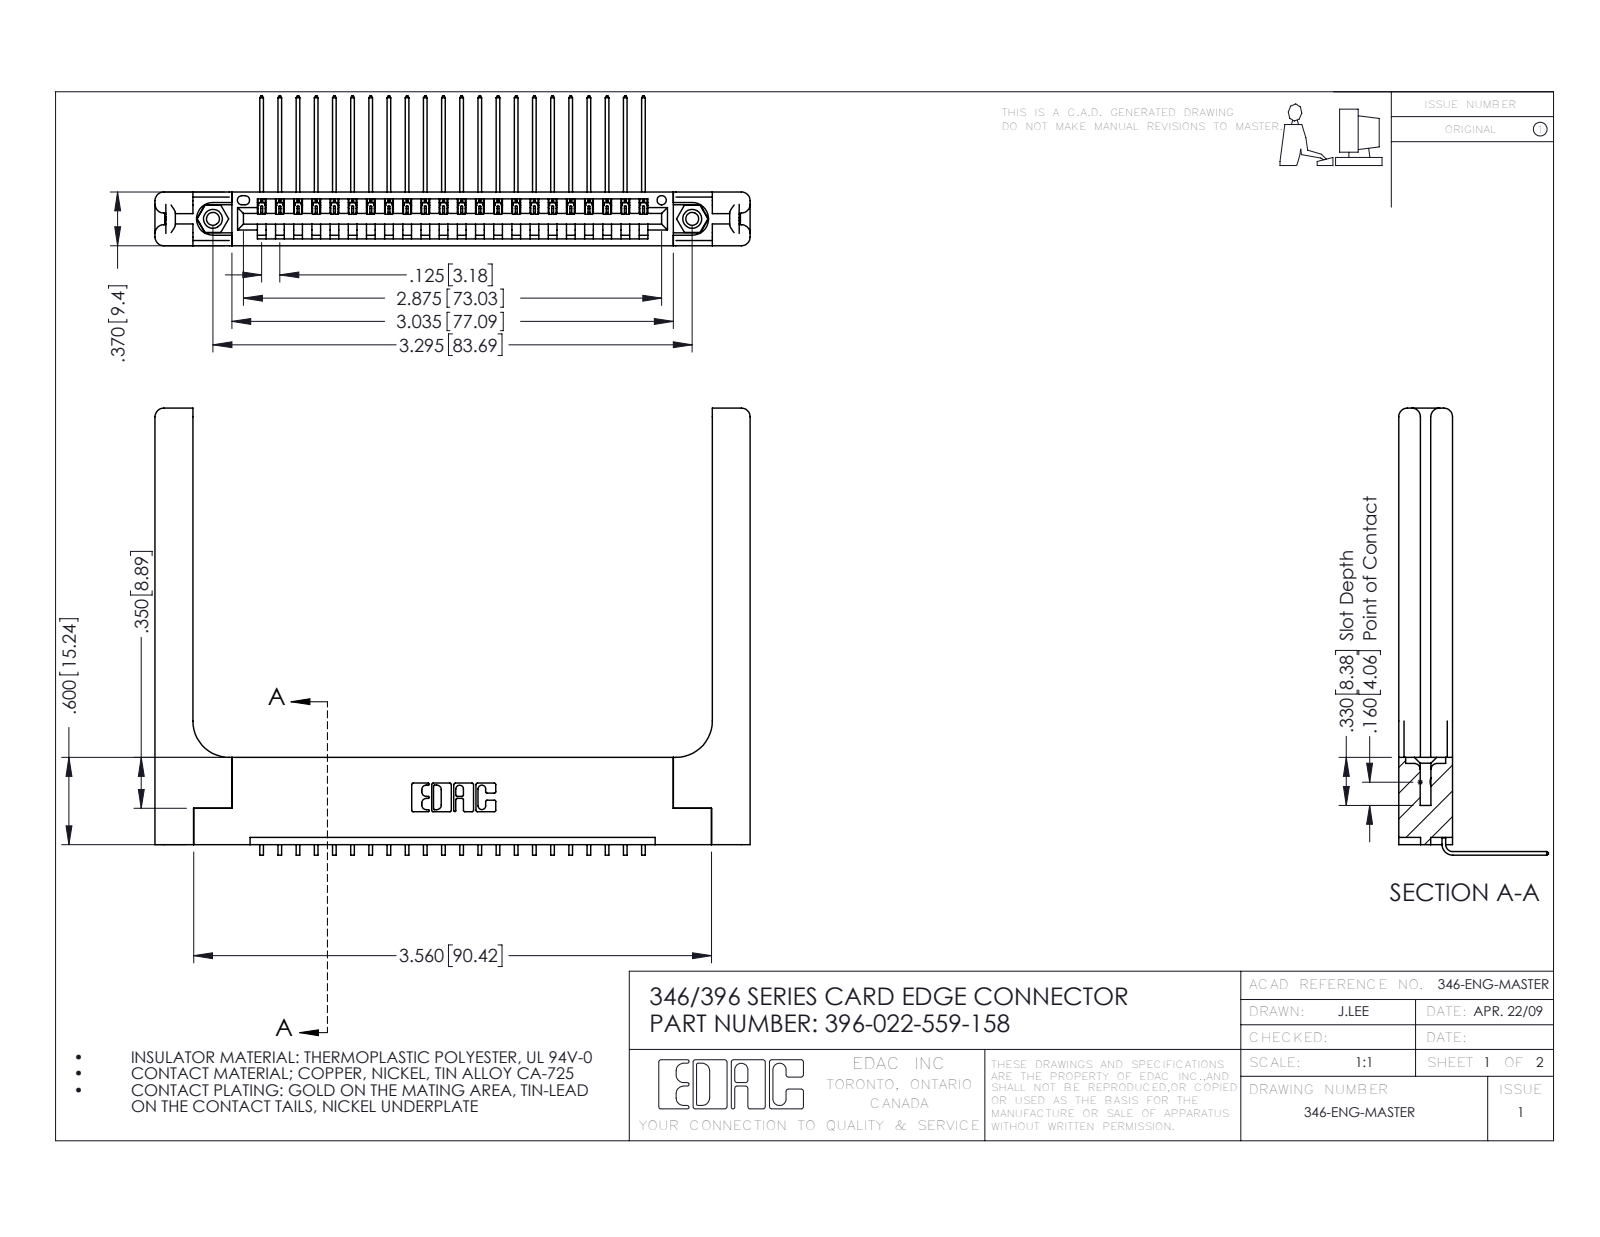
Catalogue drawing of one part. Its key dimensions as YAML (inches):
part_name: "345-292-001_558 559 Tail - 1; 346 Part_Flush Mounting Lugs - 0.156 Dia-TH; 396-022-559-158; 345-250-001_345-250-001-102 (+1 more)"
step_written_by: "SolidWorks 2016 (CONFIG_CONTROL_DESIGN)"
units: inches
bodies: {solids: 27, faces: 1698, planar: 1148, cylindrical: 490, other: 60}
overall_size: [4.091, 3.073, 1.03]
volume: 1.062
surface_area: 27.5
round_holes:
  - {diameter: 0.089, count: 2}
  - {diameter: 0.125, count: 2}
  - {diameter: 0.156, count: 2}
  - {diameter: 0.064, count: 1}
round_bosses_or_shafts:
  - {diameter: 0.155, count: 2}
partial_cylinders:
  - {radius: 0.006, count: 44}
  - {radius: 0.01, count: 22}
  - {radius: 0.06, count: 16}
  - {radius: 0.007, count: 6}
  - {radius: 0.031, count: 6}
  - {radius: 0.026, count: 3}
  - {radius: 0.03, count: 2}
  - {radius: 0.031, count: 2}
face_to_face_distances: [0.37, 0.072, 0.048, 0.322, 0.15, 0.148, 0.25, 0.025, 0.298, 0.102]
hole_center_spacings: [0.246, 3.087, 3.295]
